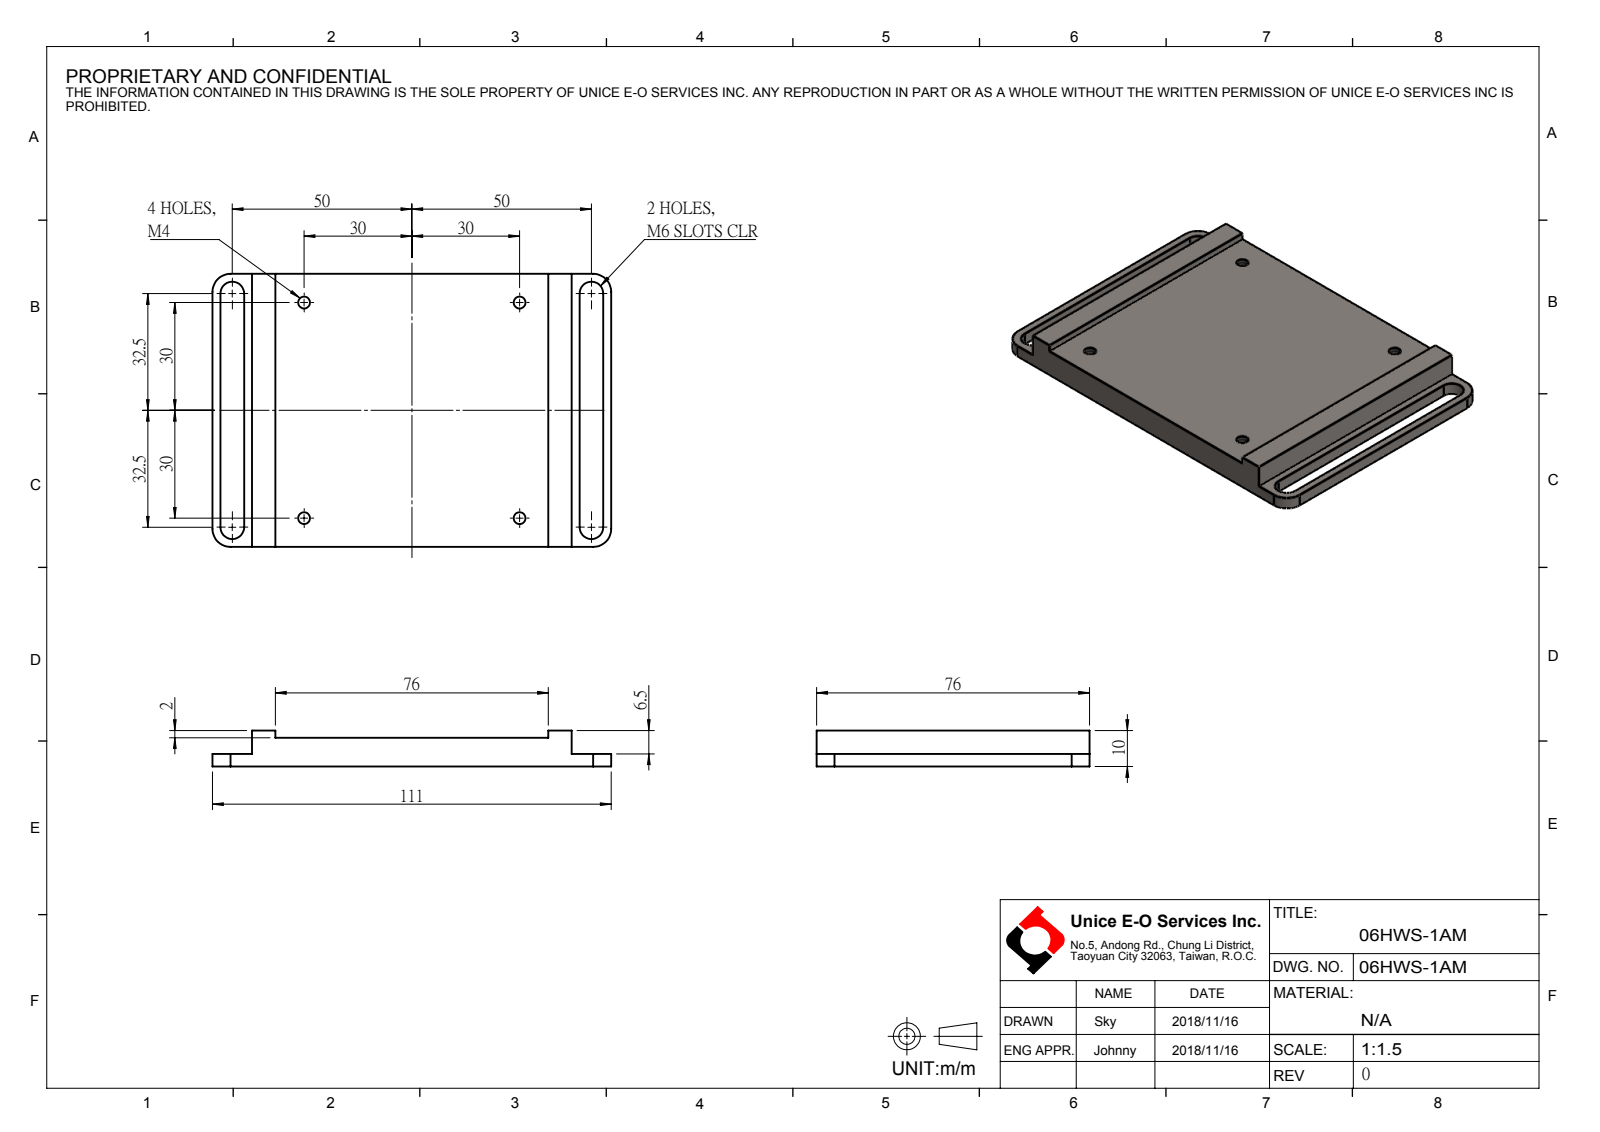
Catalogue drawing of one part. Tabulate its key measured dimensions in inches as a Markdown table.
| quantity | value |
| --- | --- |
| part name | 06HWS-1AM |
| STEP written by | SolidWorks 2016 (AUTOMOTIVE_DESIGN) |
| units | inches |
| bodies | 0 solids, 34 faces (18 planar, 16 cylindrical, 0 other) |
| overall size | 4.37 × 2.992 × 0.394 |
| round holes (diameter × count) | 0.13 × 4 |
| partial cylindrical surfaces (radius × count) | 0.13 × 4, 0.197 × 4 |
| main face-to-face distances | 0.315, 0.256, 0.394, 0.079, 2.992, 3.937, 0.087, 0.346, 0.138, 0.177 |
| hole center spacings | 2.362, 3.341 |
